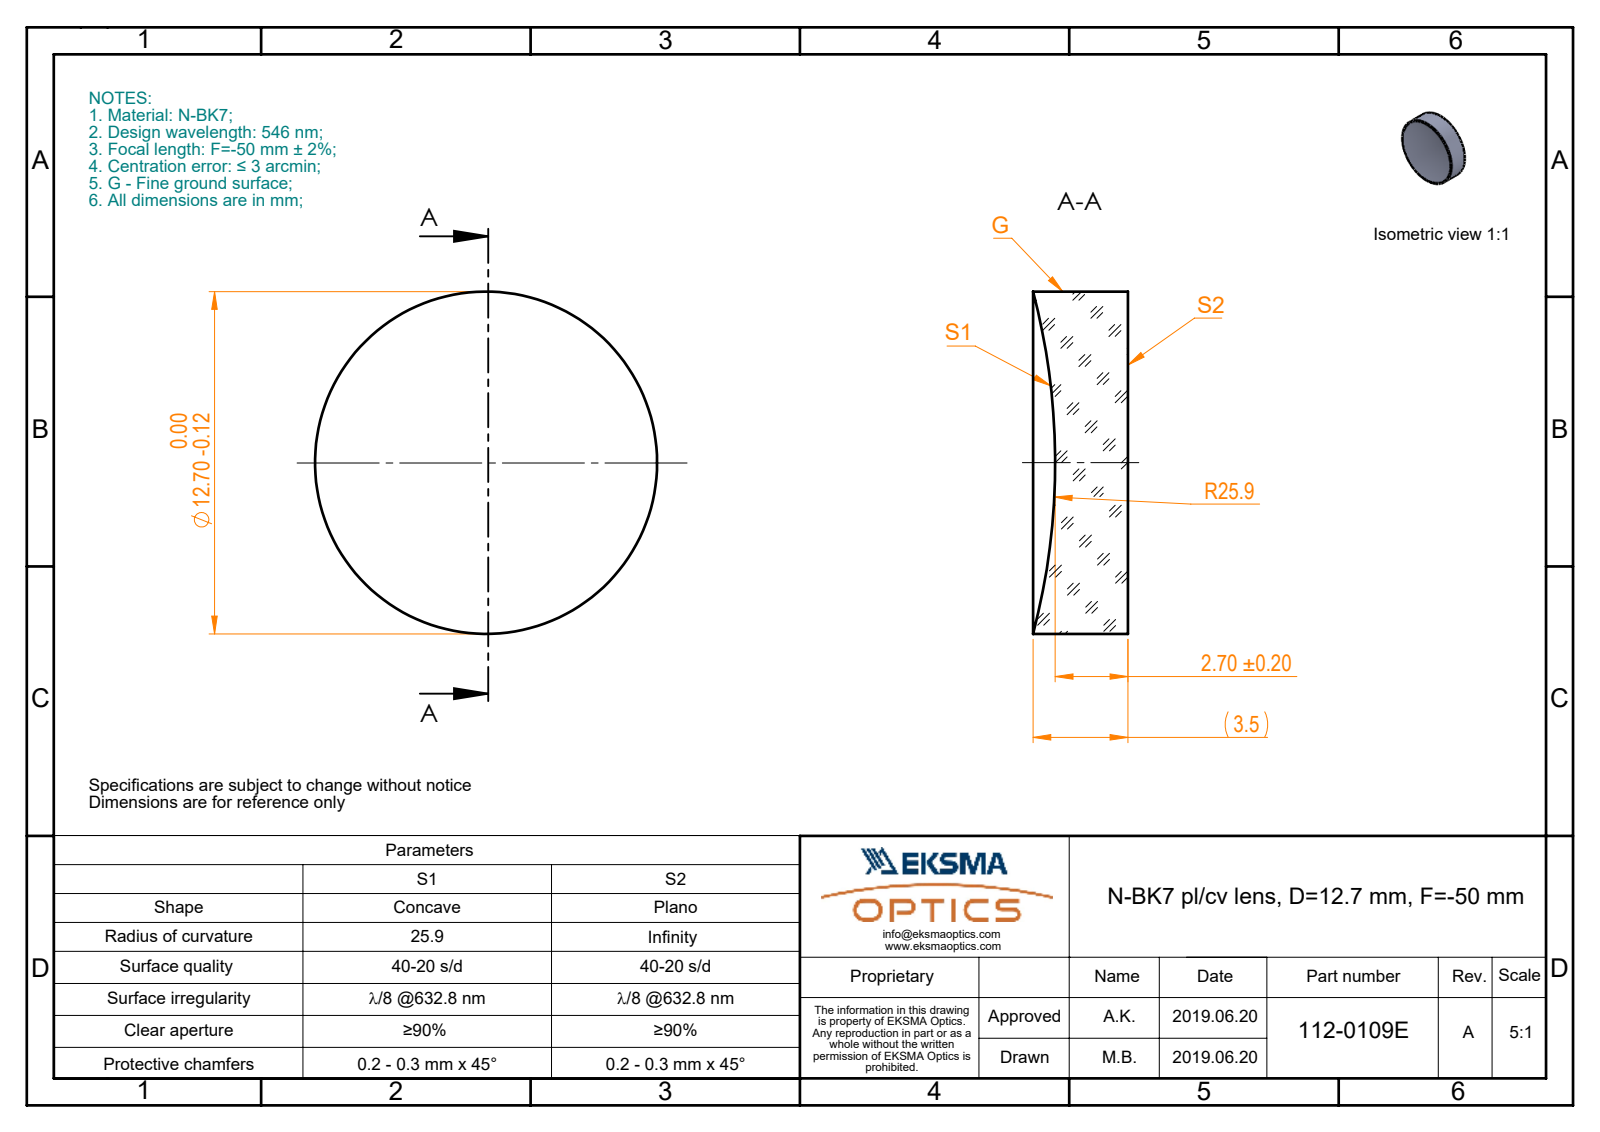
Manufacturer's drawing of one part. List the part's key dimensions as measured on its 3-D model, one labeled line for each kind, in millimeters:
Part name (STEP PRODUCT): 112-0109E BK7 pl-cv 12.7 F-50
STEP written by: SolidWorks 2017 (CONFIG_CONTROL_DESIGN)
Units: millimetres
Bodies: 1 solid, 5 faces (1 planar, 2 cylindrical, 2 other)
Overall size (bounding box): 12.7 × 12.7 × 3.52
Volume: 394 mm³ · Surface area: 396 mm²
Round bosses / shafts (diameter × count): ⌀12.7 ×1
